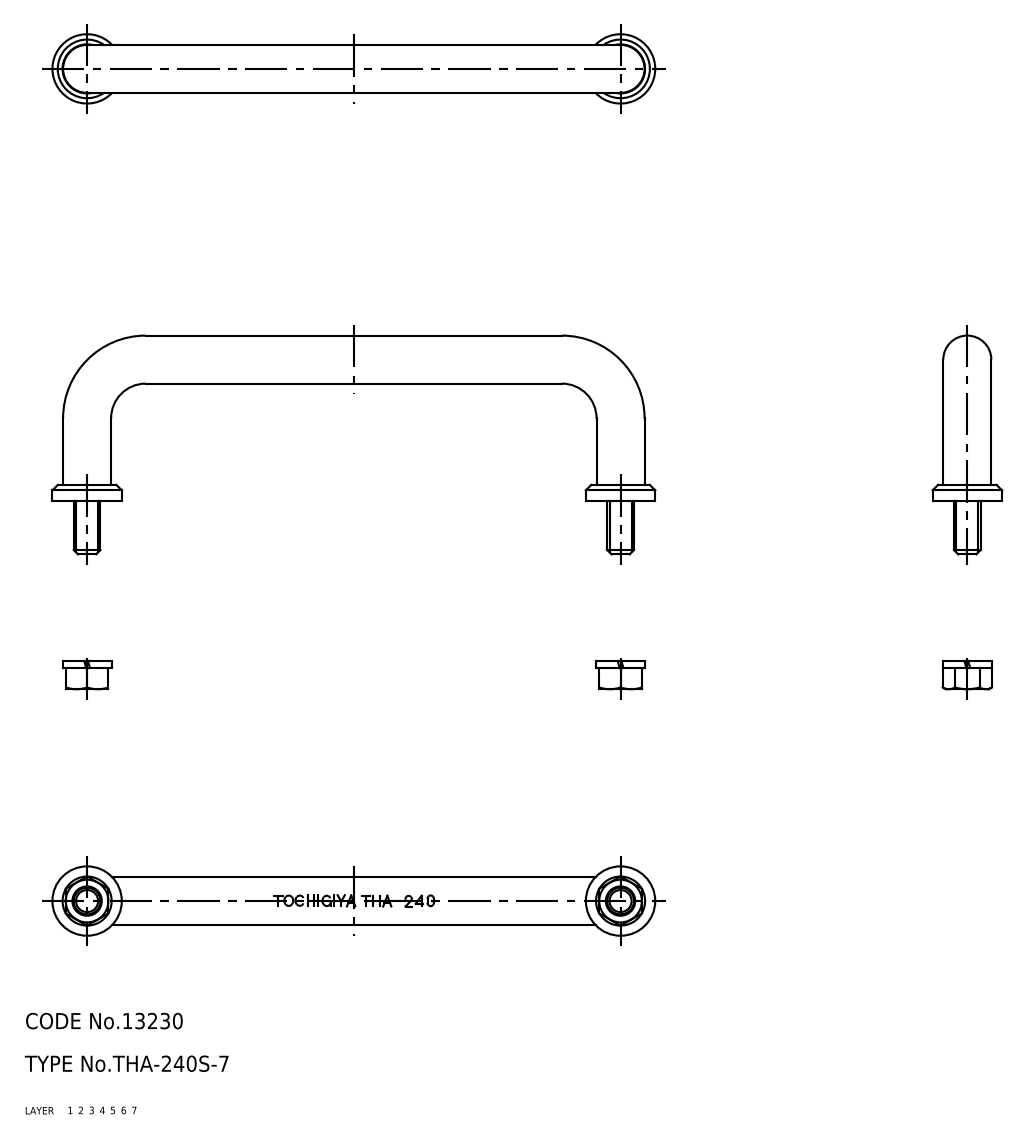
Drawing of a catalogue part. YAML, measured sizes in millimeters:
part_name: "pull; facing ring; nut; washer (+1 more)"
step_written_by: "SolidWorks 2015 (AUTOMOTIVE_DESIGN)"
units: millimeters
bodies: {solids: 7, faces: 90, planar: 30, cylindrical: 34, other: 26}
overall_size: [113, 41, 13]
volume: 10280
surface_area: 6028
round_holes:
  - {diameter: 5, count: 2}
  - {diameter: 5.5, count: 2}
  - {diameter: 9.2, count: 2}
round_bosses_or_shafts:
  - {diameter: 9, count: 3}
  - {diameter: 13, count: 2}
face_to_face_distances: [1, 3.3, 4.3, 2, 3, 8, 1.3, 50, 4, 5.3]
hole_center_spacings: [100]
